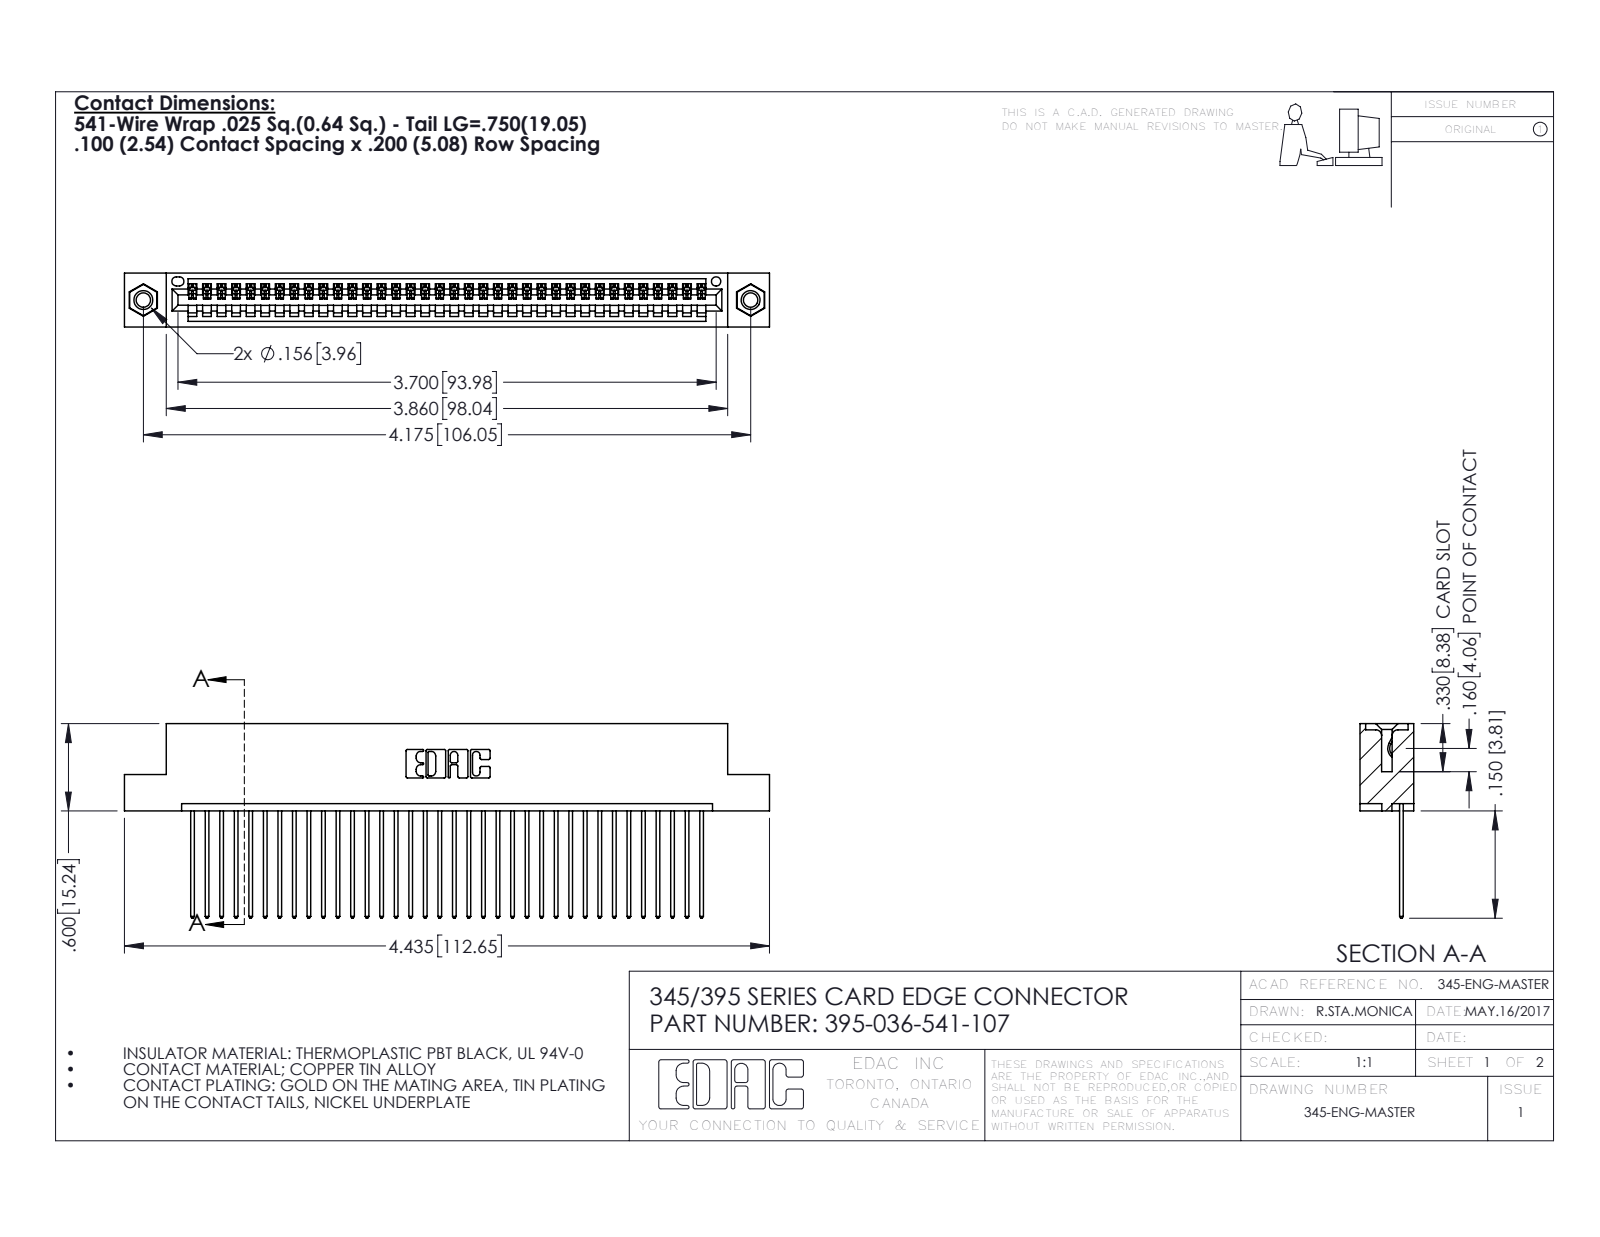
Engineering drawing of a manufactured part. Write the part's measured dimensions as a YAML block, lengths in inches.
part_name: "345 Part_Flush Mounting Lugs - 0.156 Dia-TI; 345-292-001_345-293-141; 345-250-001_345-250-005-103; 395-036-541-107"
step_written_by: "SolidWorks 2016 (CONFIG_CONTROL_DESIGN)"
units: inches
bodies: {solids: 39, faces: 2274, planar: 1552, cylindrical: 706, other: 16}
overall_size: [4.435, 1.337, 0.37]
volume: 0.656
surface_area: 23.16
round_holes:
  - {diameter: 0.098, count: 2}
  - {diameter: 0.125, count: 2}
  - {diameter: 0.156, count: 2}
  - {diameter: 0.064, count: 1}
round_bosses_or_shafts:
  - {diameter: 0.155, count: 2}
partial_cylinders:
  - {radius: 0.006, count: 72}
  - {radius: 0.01, count: 72}
  - {radius: 0.01, count: 22}
  - {radius: 0.007, count: 6}
  - {radius: 0.031, count: 6}
  - {radius: 0.026, count: 3}
  - {radius: 0.031, count: 2}
  - {radius: 0.04, count: 2}
face_to_face_distances: [0.072, 0.298, 0.098, 0.272, 0.025, 0.37, 0.2, 0.225, 0.149, 0.072]
hole_center_spacings: [0.27, 3.939, 4.175]
